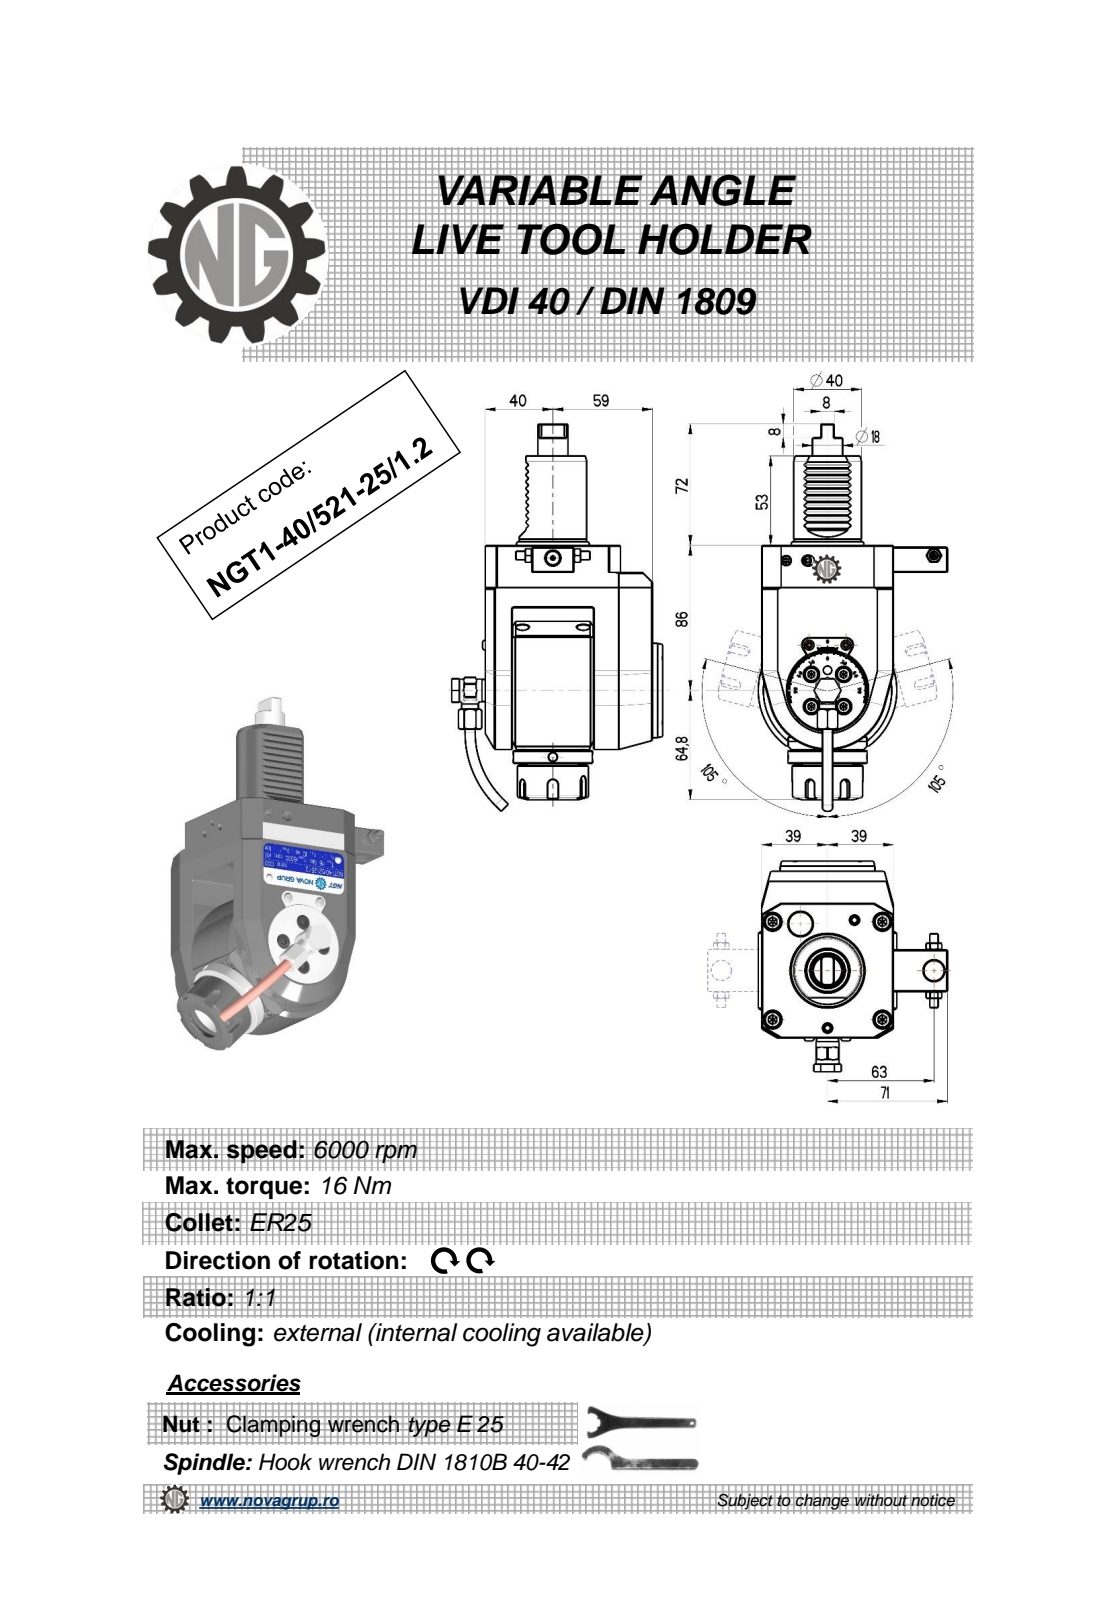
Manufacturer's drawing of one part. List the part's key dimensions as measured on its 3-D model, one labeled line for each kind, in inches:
Part name (STEP PRODUCT): NGT1_40_521_25_1_2
STEP written by: PRO/ENGINEER BY PARAMETRIC TECHNOLOGY CORPORATION, 2010280 (CONFIG_CONTROL_DESIGN)
Units: inches
Bodies: 1 solid, 575 faces (248 planar, 138 cylindrical, 189 other)
Overall size (bounding box): 9.042 × 4.917 × 4.409
Volume: 55.59 in³ · Surface area: 129.6 in²
Round holes (diameter × count): ⌀0.157 ×3, ⌀0.197 ×2, ⌀0.118 ×1, ⌀0.165 ×1, ⌀0.244 ×1, ⌀0.354 ×1, ⌀0.374 ×1, ⌀0.433 ×1, ⌀0.472 ×1, ⌀0.799 ×1
Round bosses / shafts (diameter × count): ⌀0.394 ×2, ⌀0.236 ×2, ⌀0.224 ×2, ⌀3.228 ×1, ⌀2.205 ×1, ⌀1.85 ×1, ⌀1.654 ×1, ⌀1.575 ×1
Partial cylindrical surfaces — rounded edges, fillets, slot ends (radius × count): R0.01 ×12, R0.012 ×10, R0.006 ×6, R0.118 ×5, R0.02 ×4, R0.031 ×2, R0.039 ×2, R0.394 ×2
Main face-to-face distances: 0.63, 1.457, 3.898, 3.071, 2.52, 0.236, 4.134, 1.378, 0.827, 3.504
Hole centre spacings: 0.016, 1.553, 1.929, 1.945, 2.48, 3.142, 3.152, 4.009
